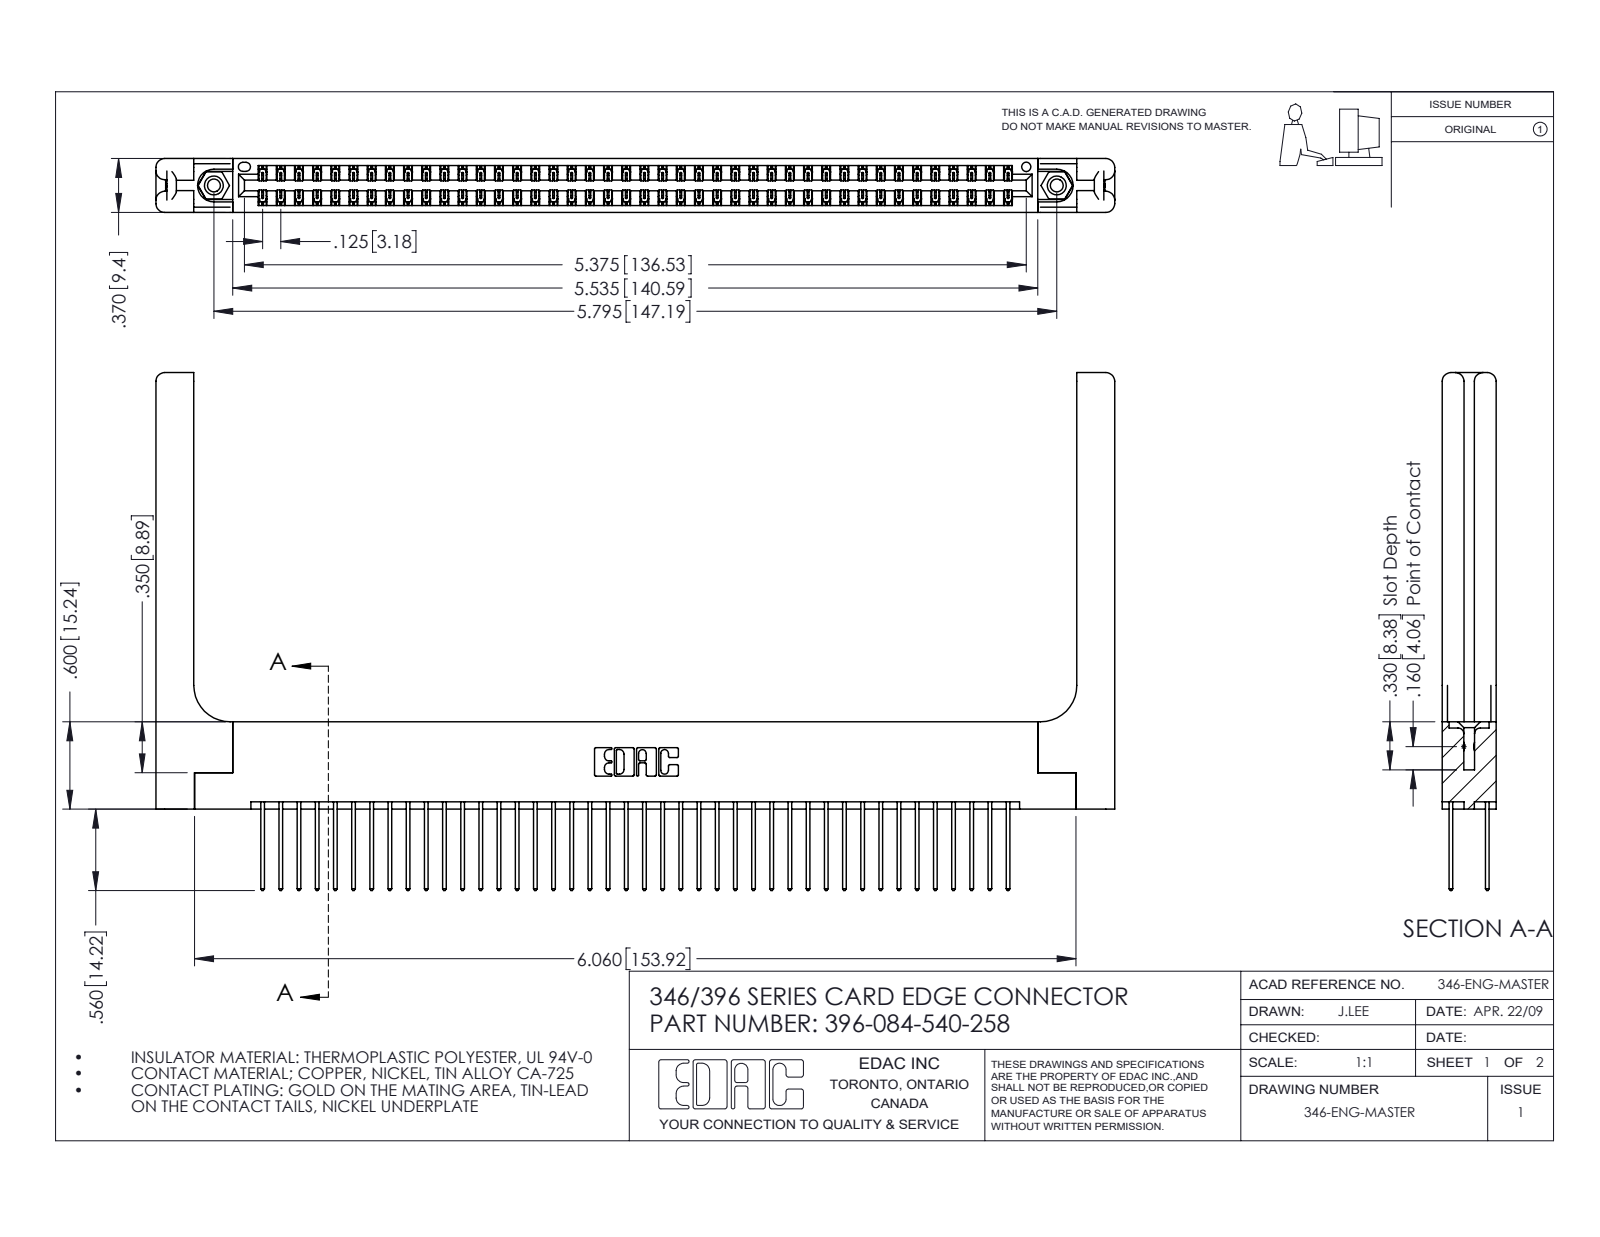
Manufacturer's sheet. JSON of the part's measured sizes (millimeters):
{"part_name": "345-292-001_345-293-140; 346-220-058_345-220-058; 396-084-540-258; 346 Part_Flush Mounting Lugs - 0.156 Dia-TH (+1 more)", "step_written_by": "SolidWorks 2016 (CONFIG_CONTROL_DESIGN)", "units": "millimeters", "bodies": {"solids": 89, "faces": 4746, "planar": 3164, "cylindrical": 1522, "other": 60}, "overall_size": [167.4, 90.4, 9.4], "volume_mm3": 24140, "surface_area_mm2": 29350, "round_holes": [[2.3, 2], [3.2, 2], [4, 2], [1.6, 1]], "round_bosses_or_shafts": [[3.9, 2]], "partial_cylinders_radius": [[0.2, 126], [0.3, 84], [0.3, 22], [1.5, 16], [0.2, 6], [0.8, 6], [0.7, 3], [0.4, 2]], "face_to_face_distances": [1.2, 8.2, 1.8, 9.4, 6.4, 0.6, 7.6, 3.8, 3.8, 7], "hole_center_spacings": [6.2, 141.9, 147.2]}
